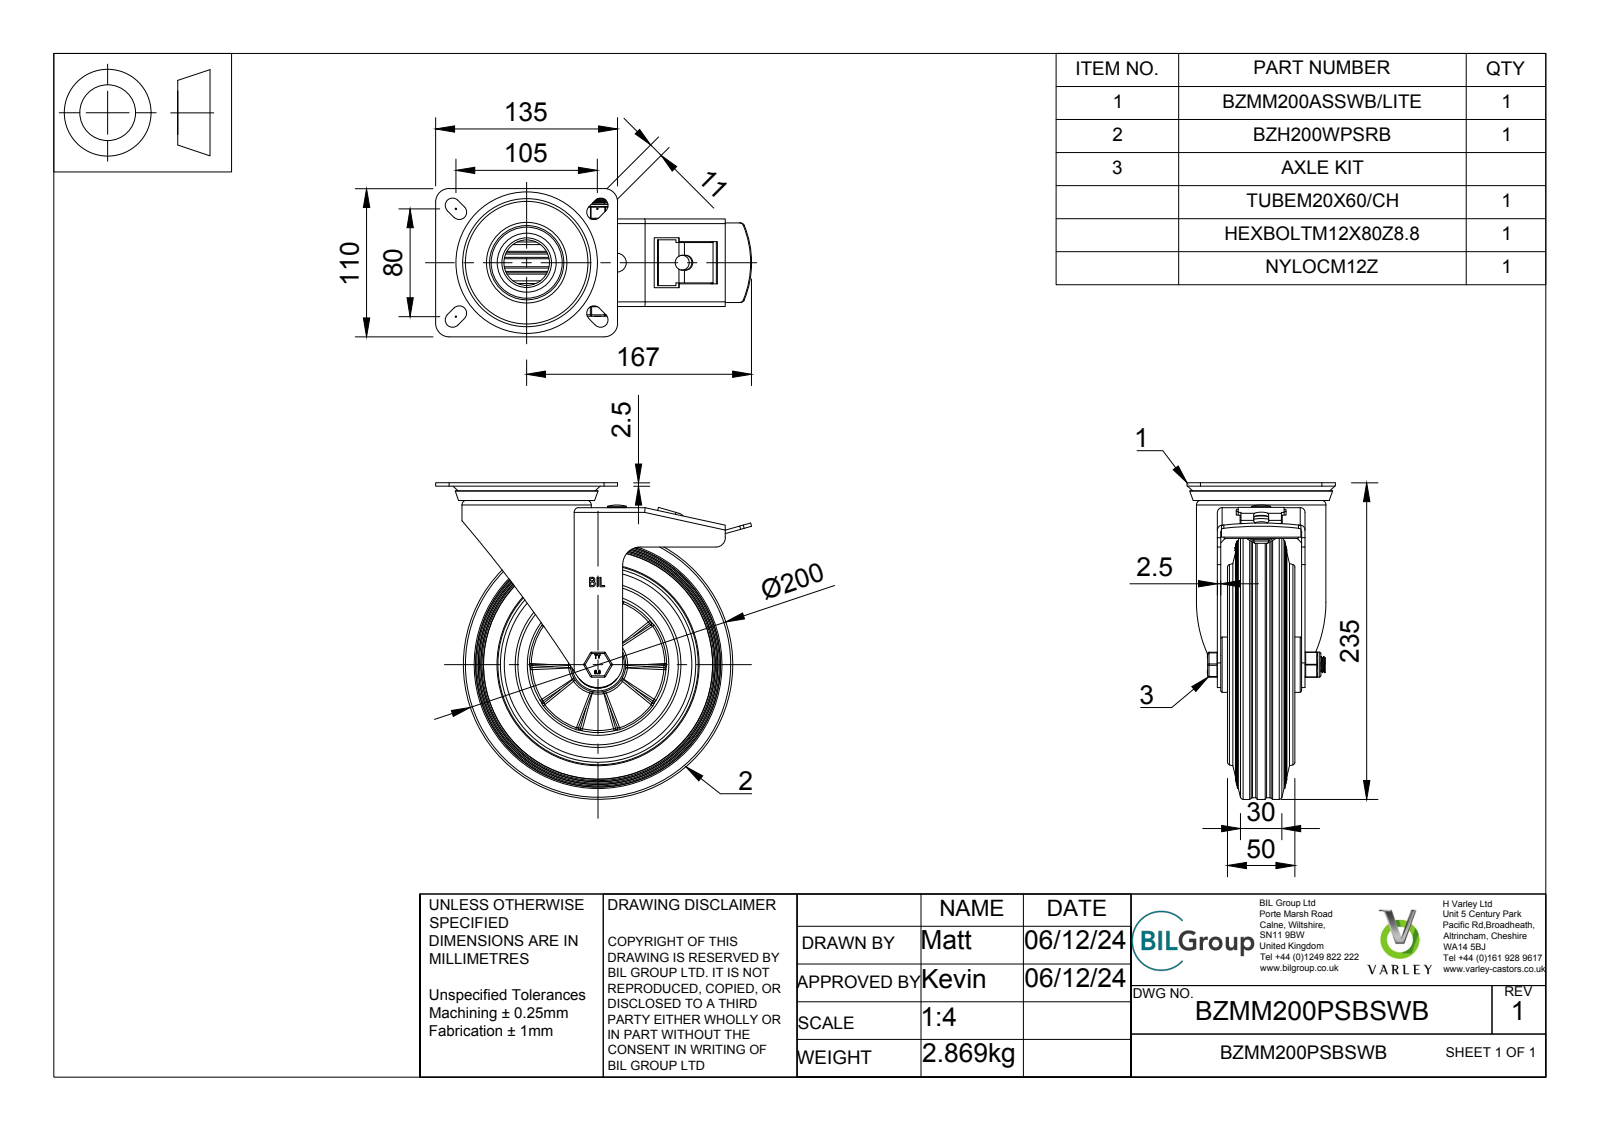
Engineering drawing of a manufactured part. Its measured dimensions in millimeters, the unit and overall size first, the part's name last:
Units: millimetres
Overall size (bounding box): 235 × 234.5 × 110
Round holes (diameter × count): ⌀8 ×1, ⌀11 ×1, ⌀12 ×1, ⌀12.2 ×1, ⌀12.5 ×1, ⌀14 ×1, ⌀20 ×1, ⌀33.75 ×1, ⌀35 ×1, ⌀61 ×1, ⌀91 ×1, ⌀101 ×1
Round bosses / shafts (diameter × count): ⌀7.5 ×8, ⌀200 ×1, ⌀197.5 ×1, ⌀123 ×1, ⌀96 ×1, ⌀78 ×1, ⌀50 ×1, ⌀41 ×1
Partial cylindrical surfaces — rounded edges, fillets, slot ends (radius × count): R0.5 ×18, R1 ×12, R5.5 ×10, R1.75 ×7, R0.25 ×6, R2.5 ×6, R3.5 ×4, R10 ×4
Main face-to-face distances: 2.5, 9, 6.5, 4, 62.5, 5, 7.5, 2, 3, 53.5
Hole centre spacings: 67
Volume: 1 257 000 mm³ · Surface area: 350 508 mm²
Bodies: 64 solids, 1002 faces (340 planar, 202 cylindrical, 460 other)
Part name (STEP PRODUCT): BZMM200PSBSWB v3; BZMM200ASSWBLITE v1; ZINC PLATED, PRESSED STEEL TOP PLATE; ZINC PLATED, PRESSED STEEL TOP PLATE Geometry (+7 more)
STEP written by: Autodesk Translation Framework v13.20.0.188 (AP242_MANAGED_MODEL_BASED_3D_ENGINEERING_MIM_LF)
